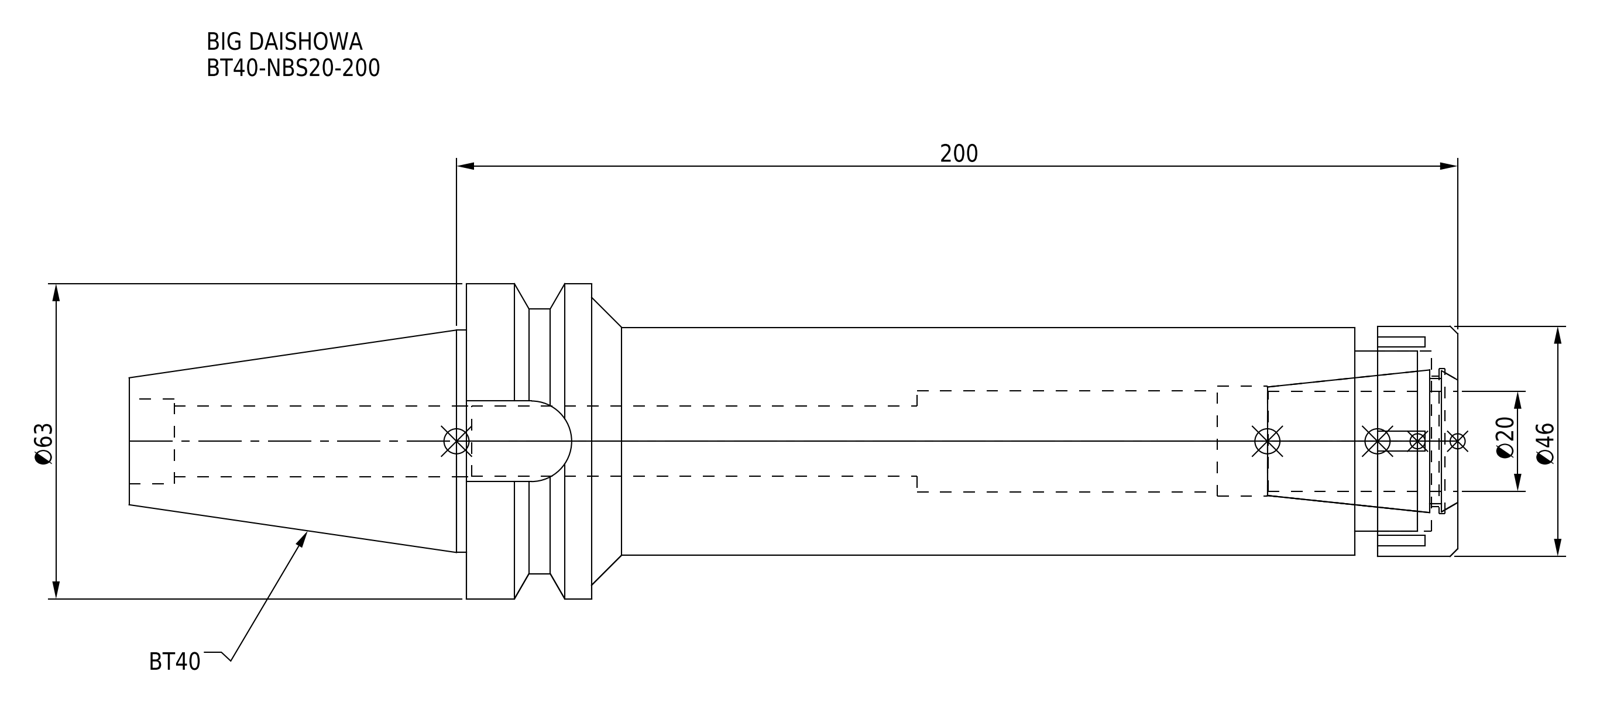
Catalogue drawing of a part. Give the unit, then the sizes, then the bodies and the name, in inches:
Units: inches
Overall size (bounding box): 10.449 × 2.48 × 2.48
Round holes (diameter × count): ⌀0.551 ×1, ⌀0.559 ×1, ⌀0.669 ×1, ⌀0.799 ×1, ⌀0.866 ×1, ⌀1.024 ×1, ⌀1.142 ×1, ⌀1.417 ×1
Round bosses / shafts (diameter × count): ⌀2.48 ×1, ⌀2.087 ×1, ⌀1.811 ×1, ⌀1.791 ×1, ⌀1.75 ×1
Partial cylindrical surfaces — rounded edges, fillets, slot ends (radius × count): R0.317 ×1
Main face-to-face distances: 7.795, 0.315, 0.807, 6.988, 0.63, 0.177, 7.165, 6.811, 6.181, 6.004
Volume: 21.15 in³ · Surface area: 95.46 in²
Bodies: 2 solids, 93 faces (45 planar, 34 cylindrical, 14 other)
Part name (STEP PRODUCT): NBN20_1.stp; BT40-NBS20-200-FreeParts; BT40-NBS20-200.stp; BT40NB20200-200_ASM.stp (+3 more)
STEP written by: SolidWorks 2019 (CONFIG_CONTROL_DESIGN)
